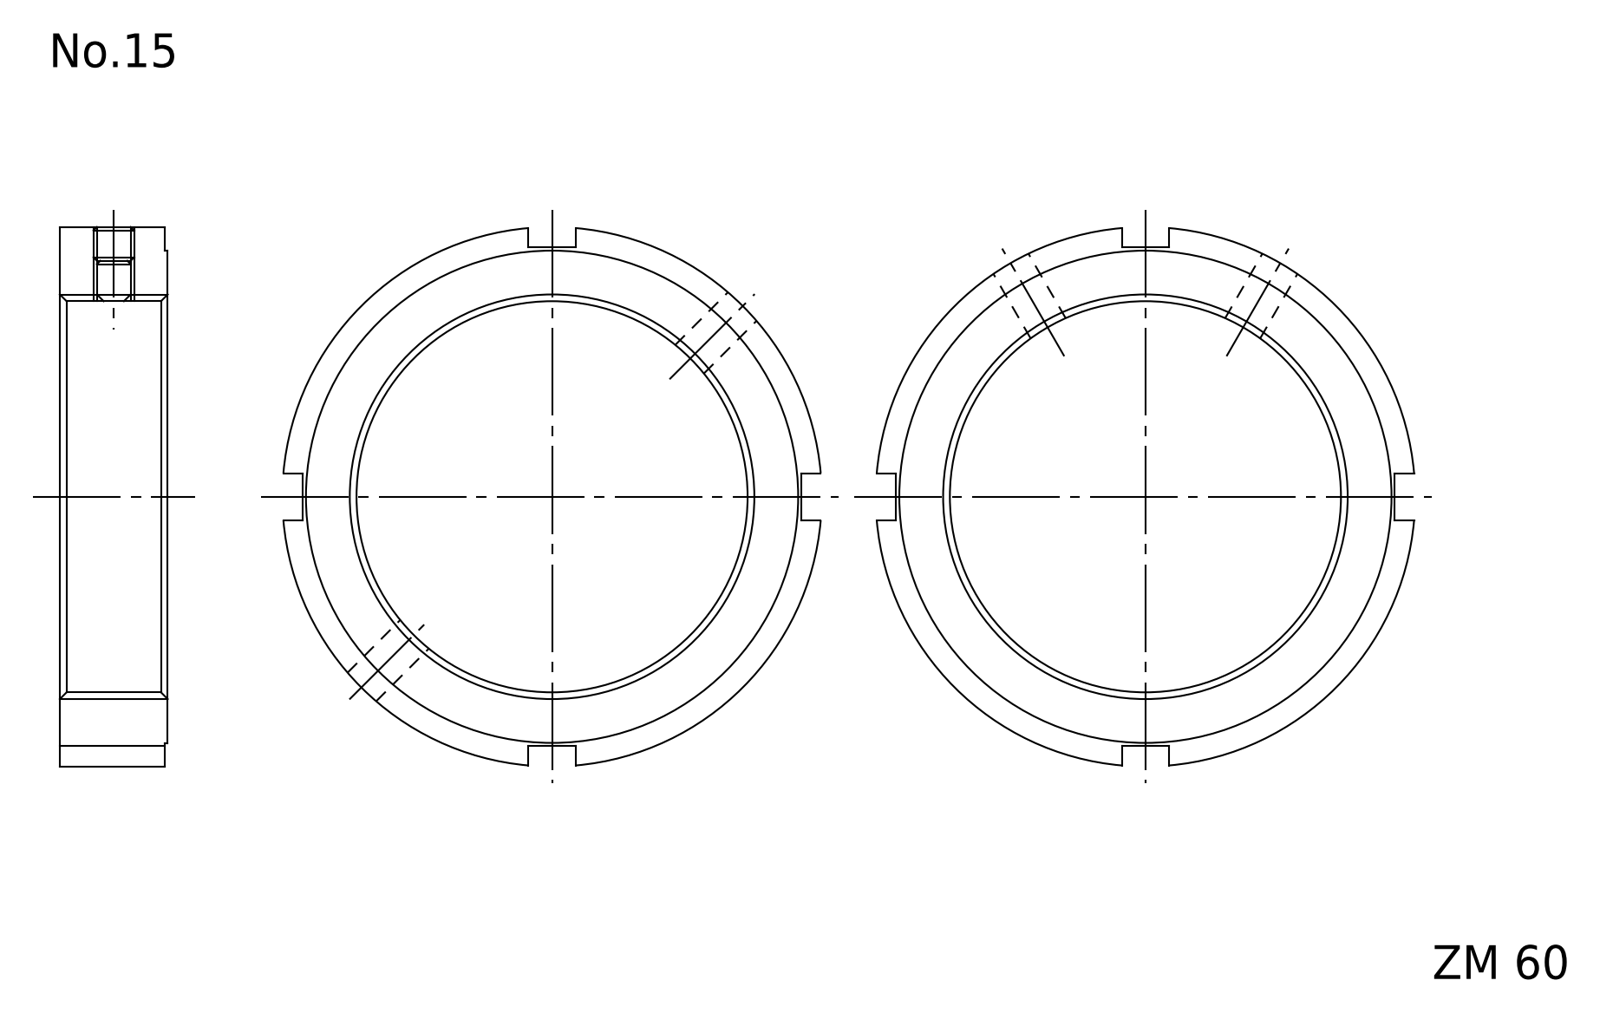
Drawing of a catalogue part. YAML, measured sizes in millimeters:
part_name: "FKD ZM 60"
step_written_by: "Autodesk Inventor 2011 (AUTOMOTIVE_DESIGN)"
units: millimeters
bodies: {solids: 1, faces: 23, planar: 15, cylindrical: 8, other: 0}
overall_size: [79.69, 79.69, 16]
volume: 33106
surface_area: 11845
round_holes:
  - {diameter: 4.92, count: 2}
  - {diameter: 60, count: 1}
round_bosses_or_shafts:
  - {diameter: 80, count: 1}
  - {diameter: 73, count: 1}
face_to_face_distances: [16, 0.5, 15.5, 33.5, 40.5, 74, 7]
